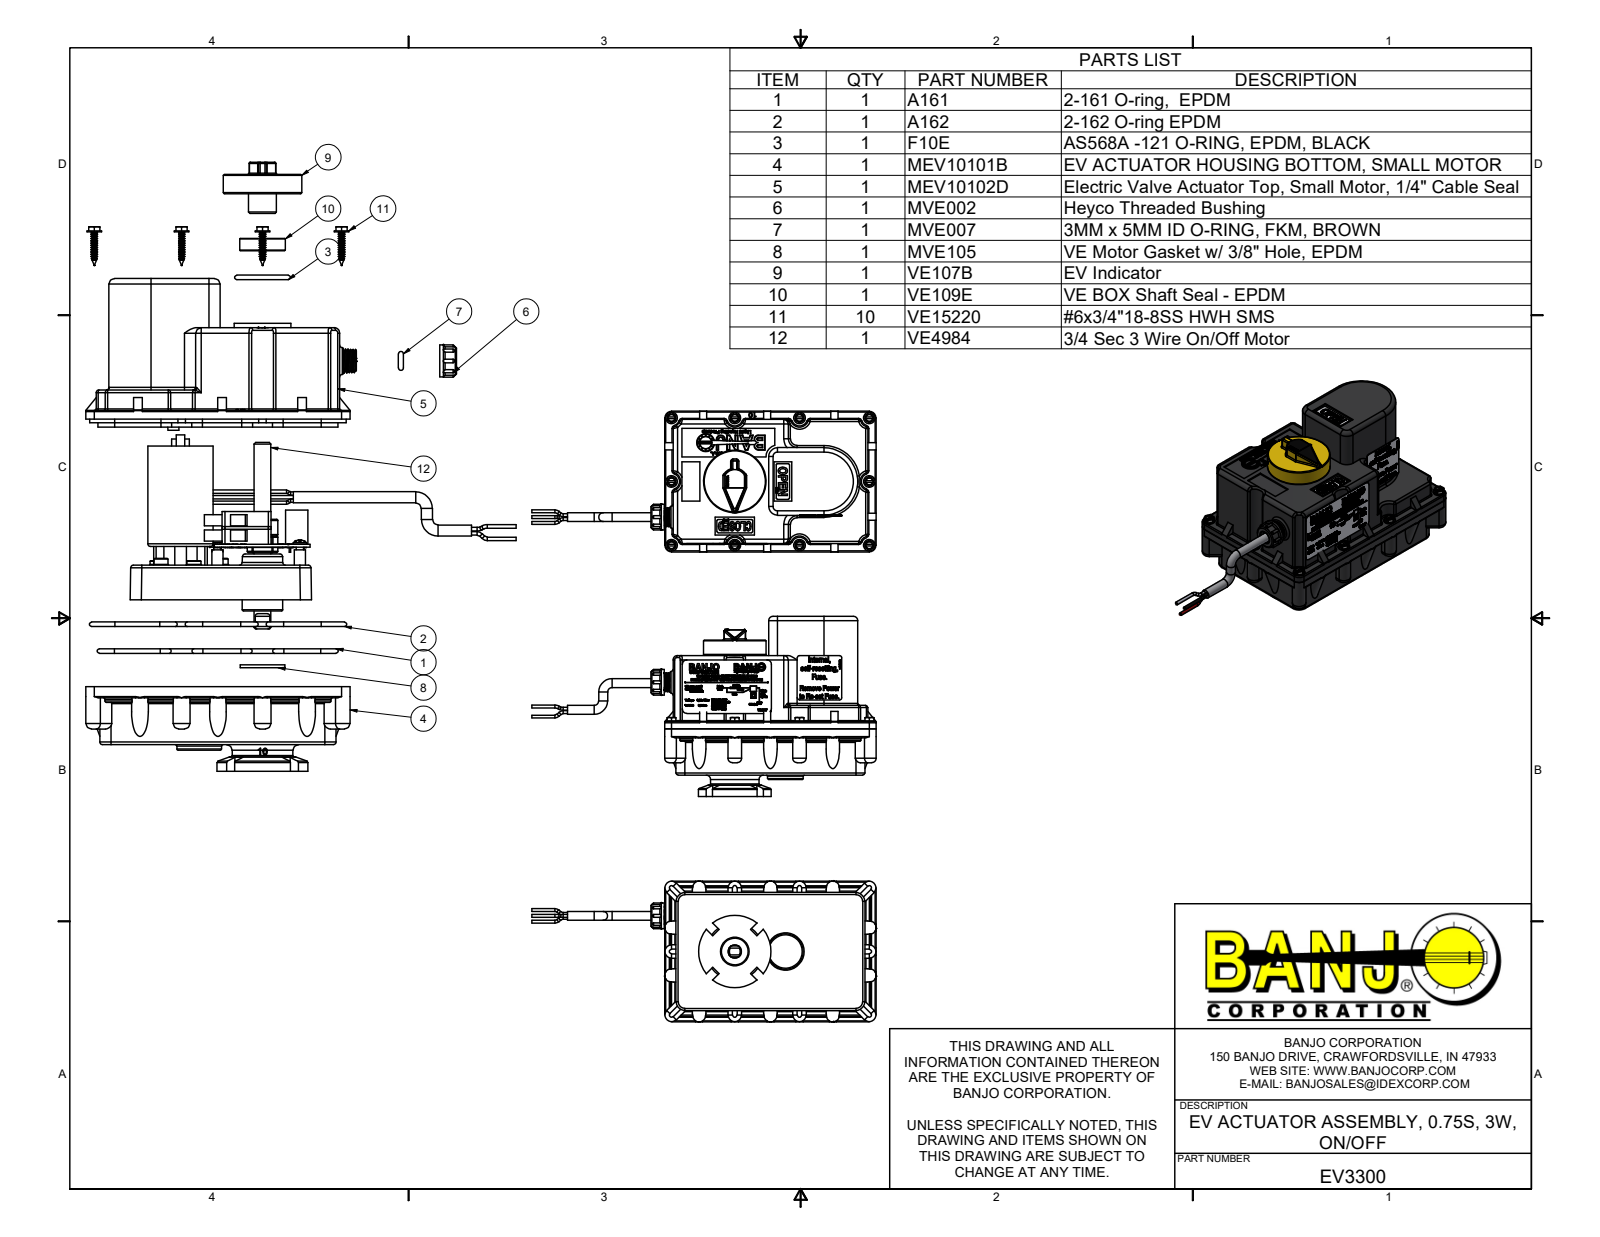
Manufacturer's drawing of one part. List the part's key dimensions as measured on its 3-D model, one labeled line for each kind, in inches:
Part name (STEP PRODUCT): EV3300; MEV10101B; MEV10102D; MEV10102DX (+8 more)
STEP written by: Autodesk Inventor 2022 (AUTOMOTIVE_DESIGN)
Units: inches
Bodies: 43 solids, 10443 faces (5437 planar, 1178 cylindrical, 3828 other)
Overall size (bounding box): 9.656 × 5.055 × 3.95
Volume: 34.6 in³ · Surface area: 397.2 in²
Round holes (diameter × count): ⌀0.11 ×10, ⌀0.16 ×10, ⌀0.2 ×10, ⌀0.052 ×8, ⌀0.079 ×8, ⌀0.047 ×6, ⌀0.12 ×6, ⌀0.15 ×6, ⌀0.176 ×6, ⌀0.015 ×4, ⌀0.04 ×3, ⌀0.17 ×3
Round bosses / shafts (diameter × count): ⌀0.328 ×10, ⌀0.138 ×10, ⌀0.08 ×9, ⌀0.103 ×8, ⌀0.25 ×7, ⌀0.075 ×5, ⌀0.316 ×4, ⌀0.025 ×4
Partial cylindrical surfaces — rounded edges, fillets, slot ends (radius × count): R0.03 ×122, R0.02 ×62, R0.06 ×47, R0.035 ×43, R0.125 ×28, R0.315 ×24, R0.5 ×24, R0.39 ×16
Main face-to-face distances: 0.125, 3.355, 1.1, 0.2, 0.79, 1.025, 3.23, 1.3, 2.565, 0.045
Hole centre spacings: 1.68, 2.058, 1.684, 1.785, 2.376, 0.109, 0.492, 1.188
